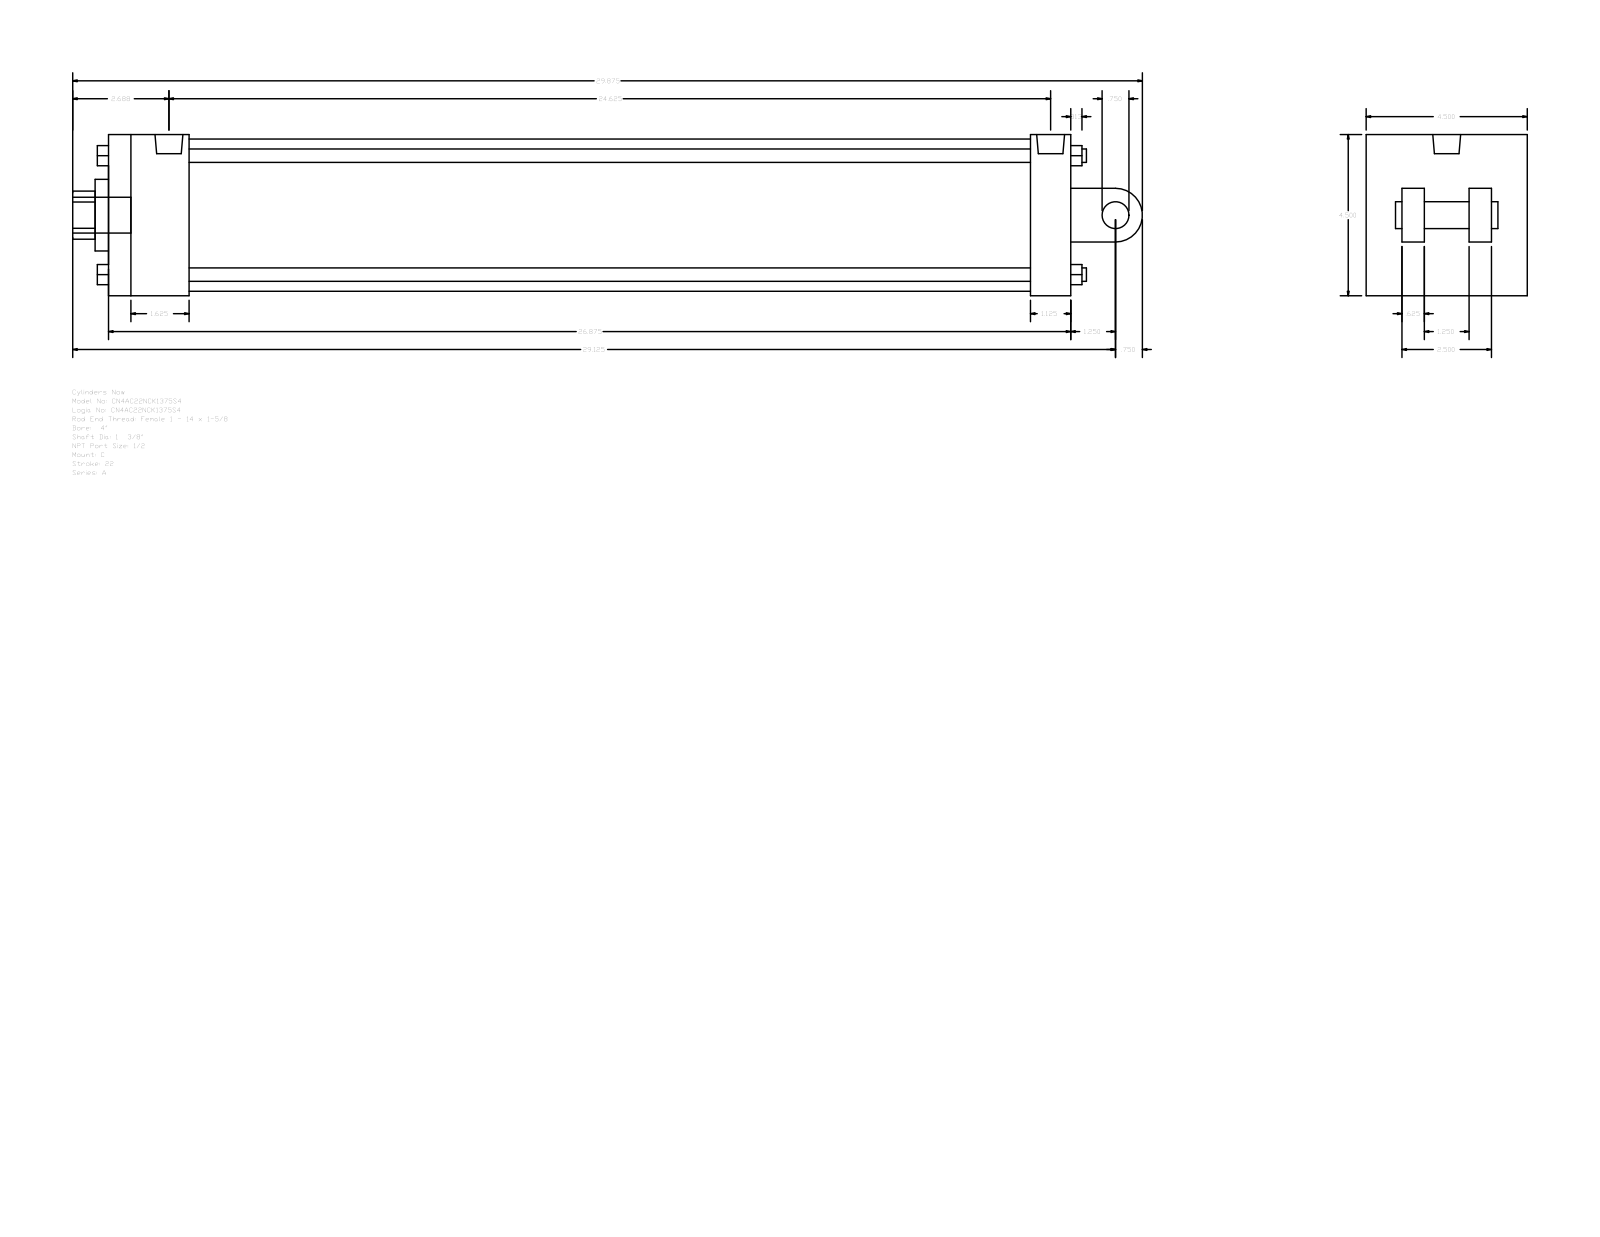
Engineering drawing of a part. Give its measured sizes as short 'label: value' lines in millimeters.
name: A_C__0400_1.375
written by: GSSL Pune (CONFIG_CONTROL_DESIGN)
unit: mm
bodies: 0 solids, 135 faces (102 planar, 33 cylindrical, 0 other)
size: 758.83 × 114.3 × 114.3
holes: 2× ⌀8.73, 1× ⌀19.77, 1× ⌀34.92, 1× ⌀50.8, 1× ⌀107.95
bosses: 4× ⌀9.53, 2× ⌀8.73, 1× ⌀25.4, 1× ⌀19.77, 1× ⌀19.05
rounds: 1× R17.06, 1× R19.05
face distances: 114.3, 682.62, 73.03, 28.57, 654.05, 57.15, 596.9, 625.47, 15.87, 41.27
hole spacings: 3.18
